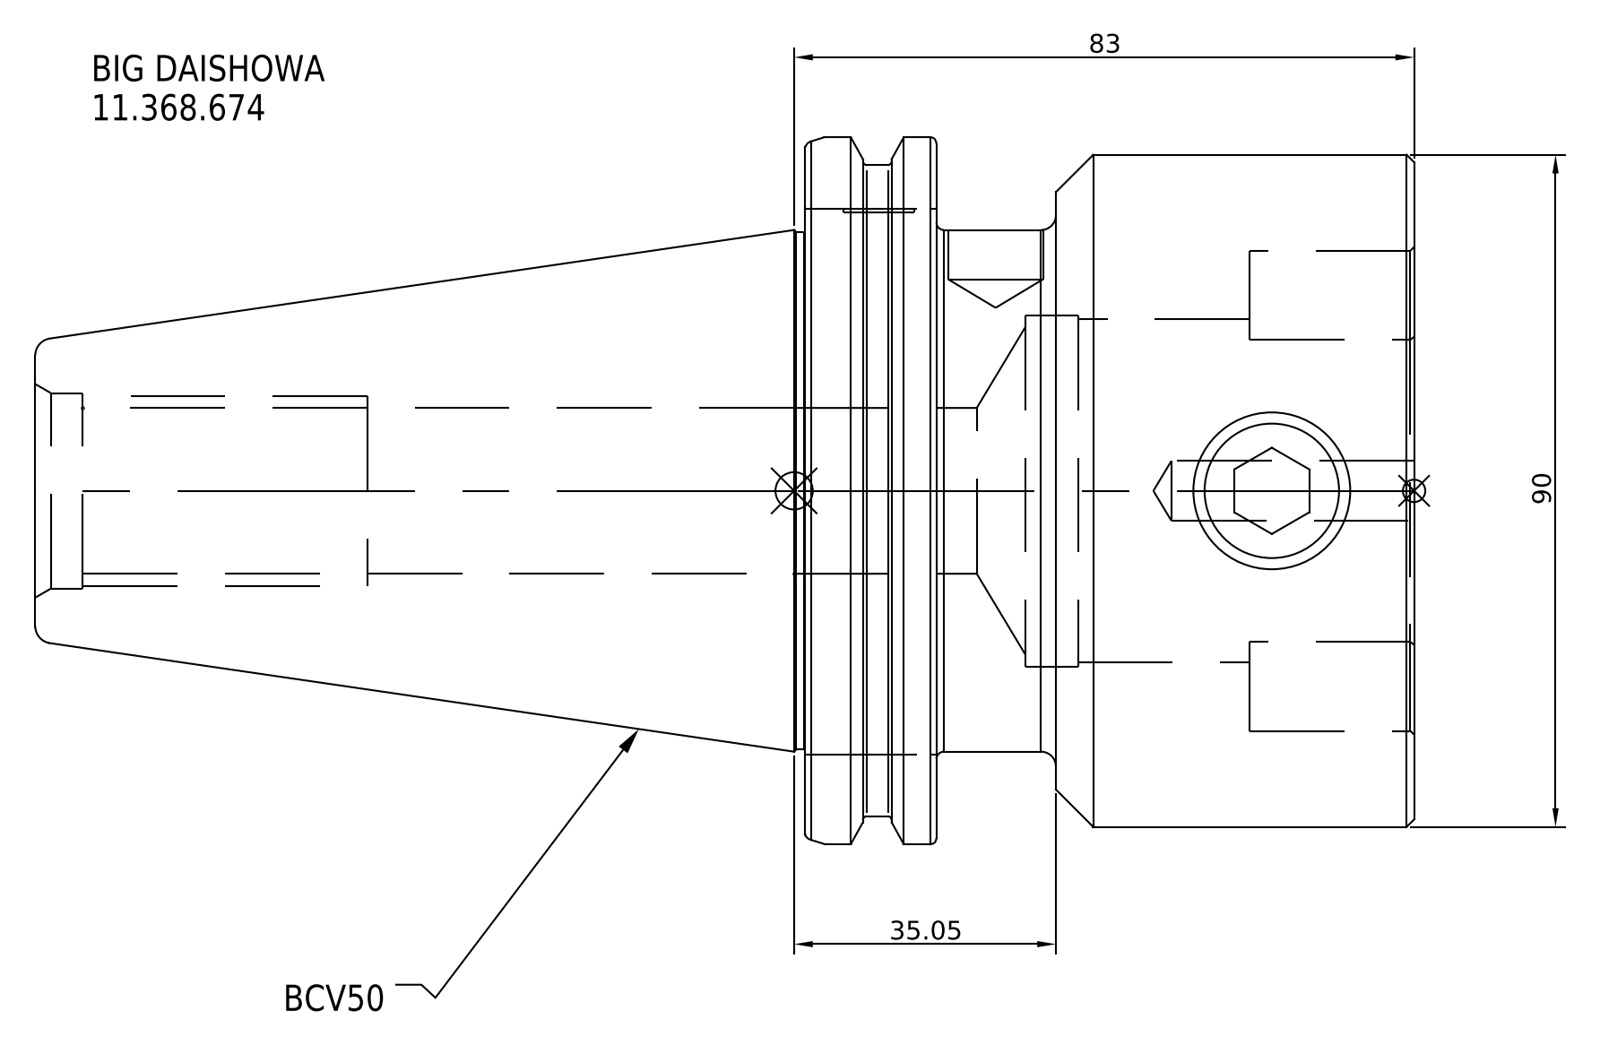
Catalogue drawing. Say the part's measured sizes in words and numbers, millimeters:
The part is named "11.368.674". Its 3-D file was written by "SolidWorks 2021 (CONFIG_CONTROL_DESIGN)". It is 1 solid with 16 faces: 7 planar, 6 cylindrical and 3 other. Overall it measures 184.6 by 98.43 by 98.43 millimeters. Its volume is 747 843 cubic millimeters and its surface area 59 604 square millimeters. Round bosses or shafts: 1 of diameter 98.43, 1 of diameter 91.29, 1 of diameter 90, 1 of diameter 69.85. The main face-to-face distances are 81.5, 63.95, 17.55, 48, 15.95, 33.5, 184.6, 136.6, 120.65, 103.1.
